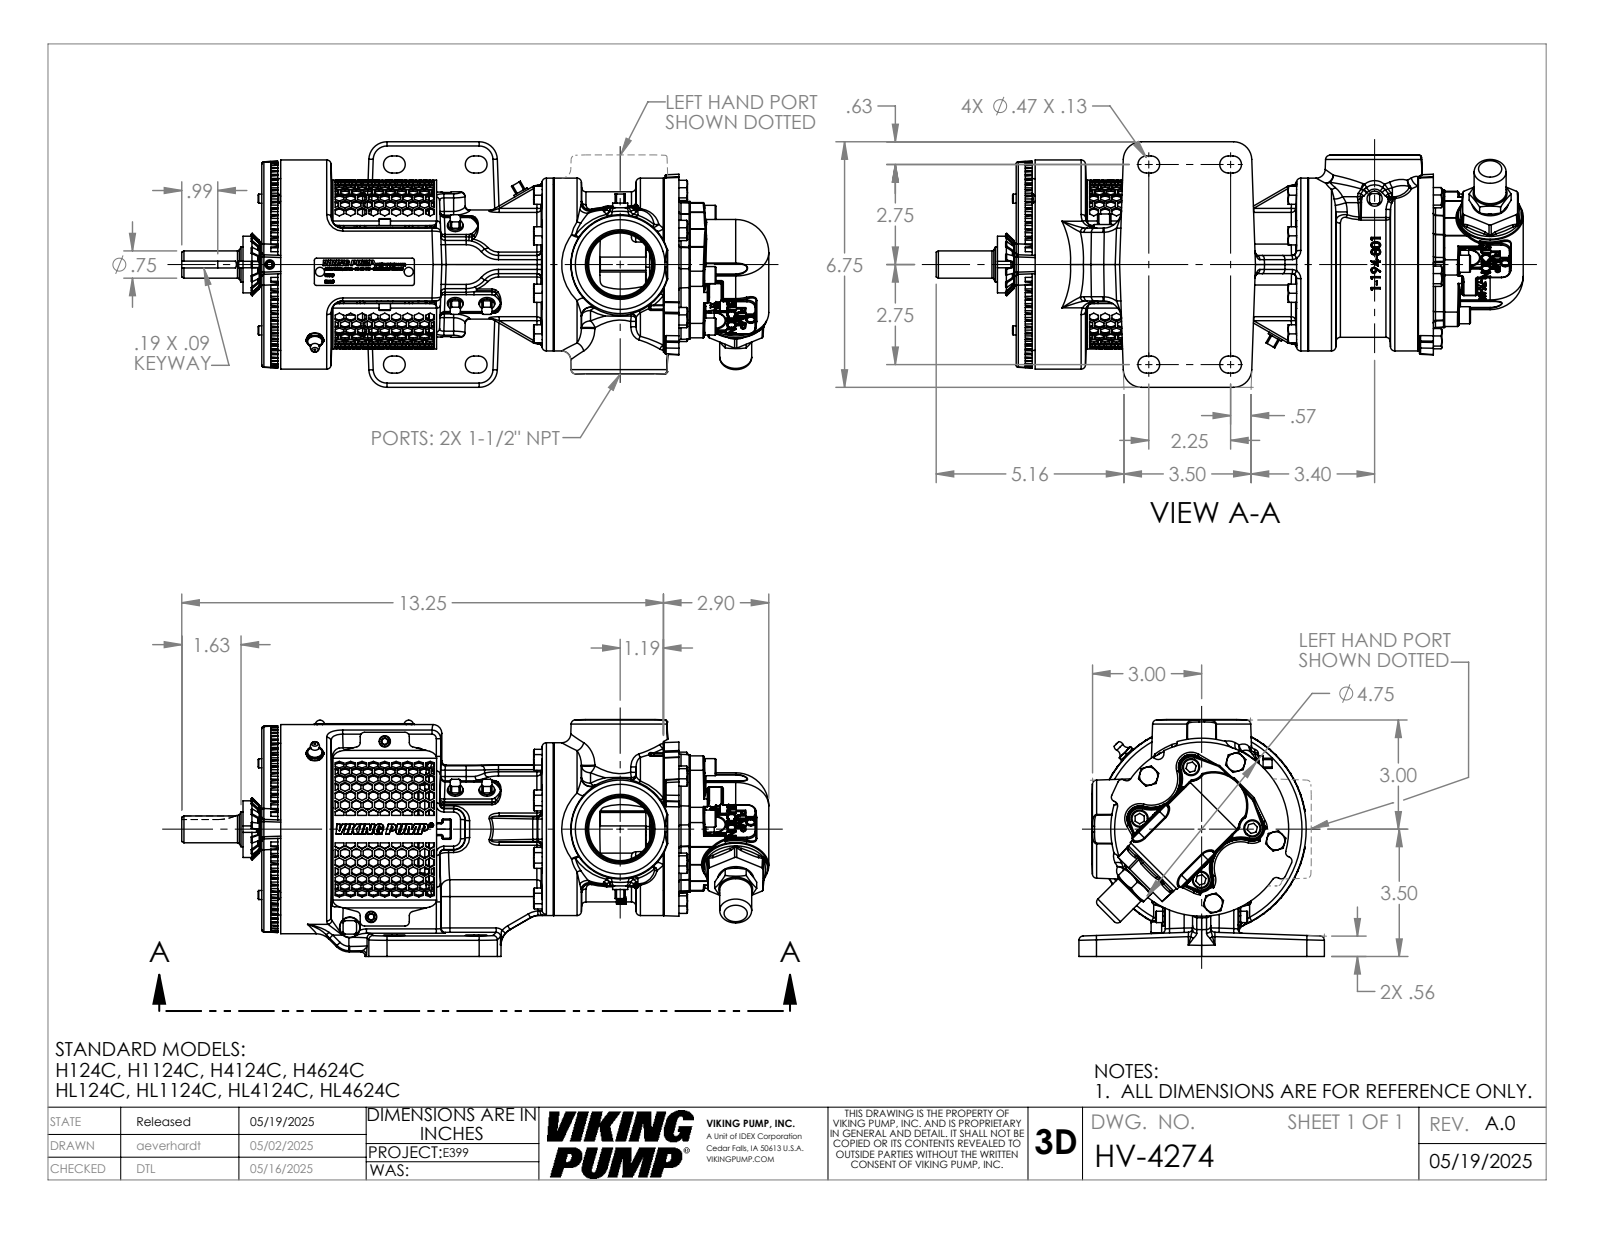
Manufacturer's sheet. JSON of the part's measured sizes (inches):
{"part_name": "HV-4274", "step_written_by": "SolidWorks 2024 (AUTOMOTIVE_DESIGN)", "units": "inches", "bodies": {"solids": 1, "faces": 4470, "planar": 1576, "cylindrical": 890, "other": 2004}, "overall_size": [16.143, 6.75, 6.515], "volume_in3": 185.4, "surface_area_in2": 512.6, "round_holes": [[0.25, 5], [0.34, 4], [0.159, 3], [0.257, 2], [0.986, 1], [0.989, 1], [4.502, 1]], "round_bosses_or_shafts": [[0.469, 4], [0.313, 4], [0.437, 3], [0.312, 3], [0.25, 2], [5.75, 1], [4.75, 1], [4.747, 1]], "partial_cylinders_radius": [[0.054, 140], [0.12, 96], [0.03, 94], [0.06, 49], [0.5, 20], [0.24, 11], [0.234, 8], [0.25, 8]], "face_to_face_distances": [1.94, 11.472, 9.531, 0.522, 1.419, 10.95, 1.5, 0.44, 0.081, 11.031], "hole_center_spacings": [2.56, 4.434, 1.224, 1.393, 1.524, 1.728, 1.878, 2]}
